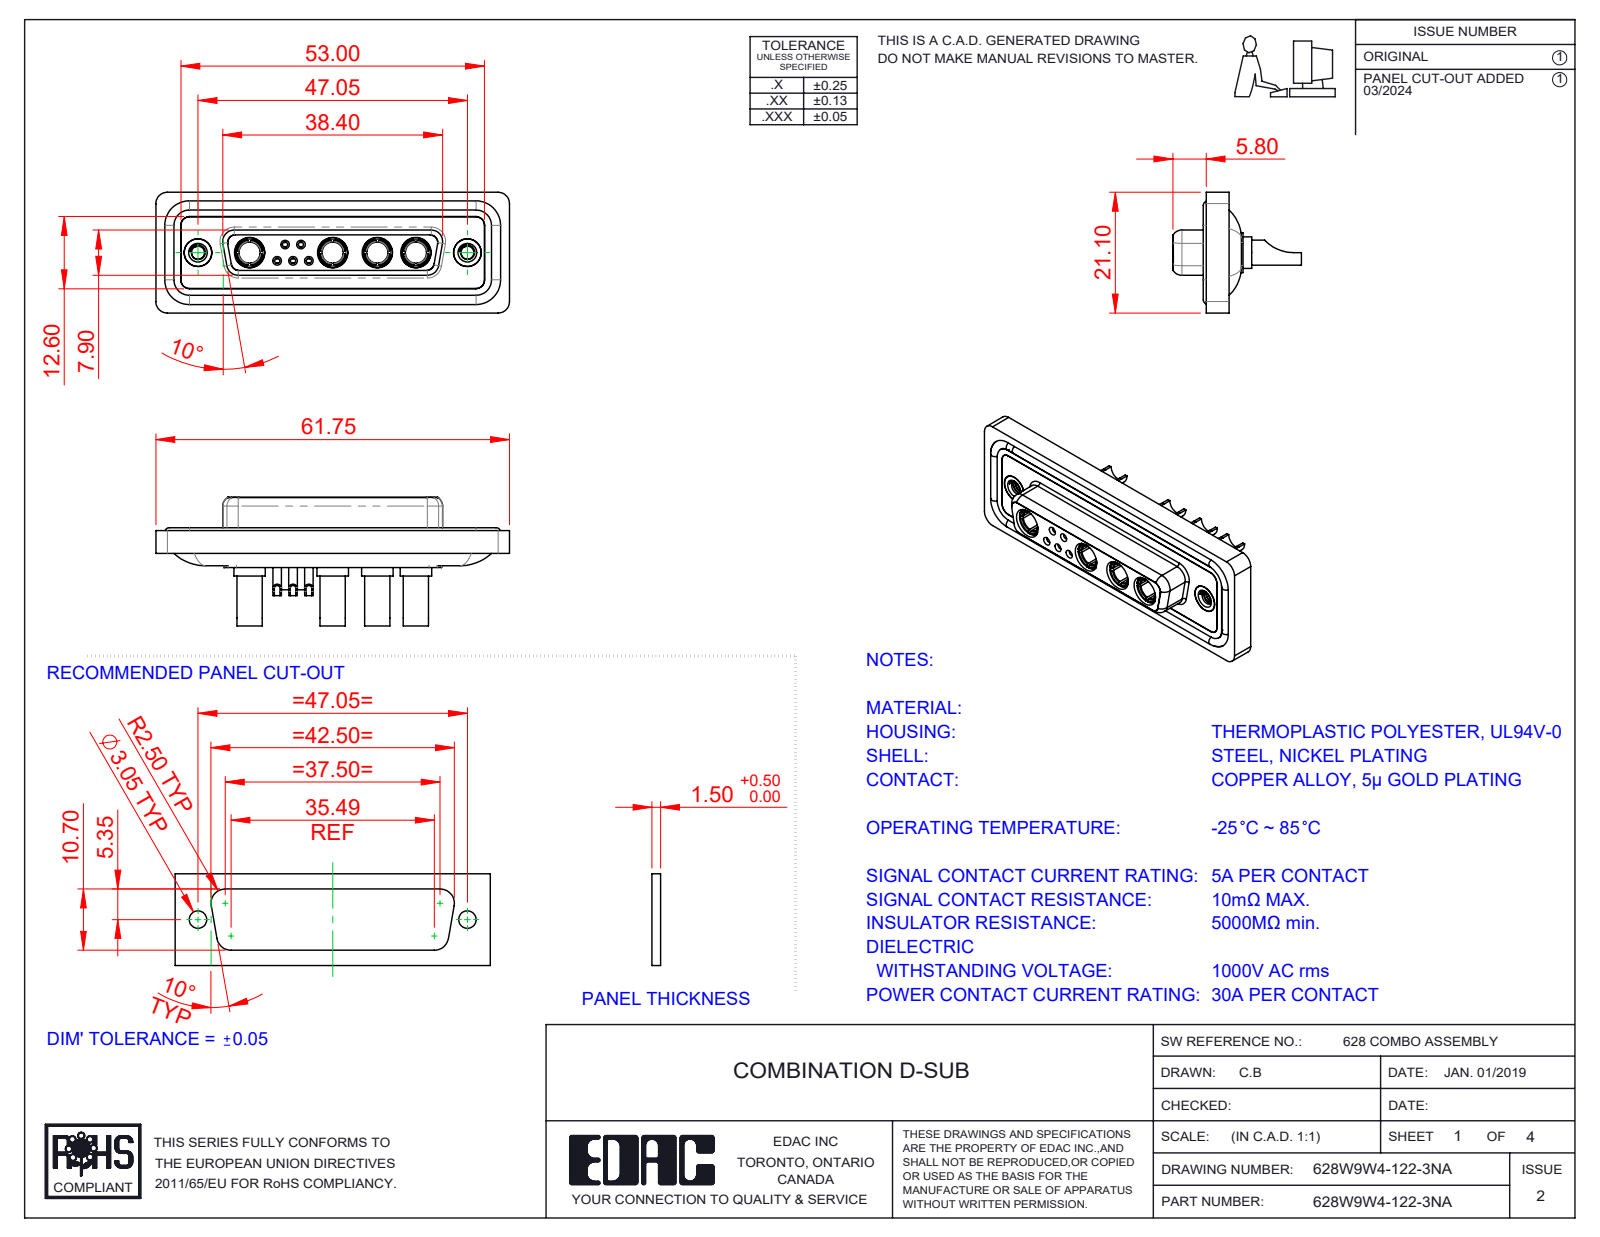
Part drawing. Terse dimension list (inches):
name: 628Combo Threaded Rivet_A; 628Combo Shell Front_25 Contacts; 628Combo Contact Row 2_22; 628Combo Waterproof Housing_25 Contacts (+5 more)
written by: SolidWorks 2023 (CONFIG_CONTROL_DESIGN)
unit: in
bodies: 20 solids, 979 faces (318 planar, 399 cylindrical, 262 other)
size: 2.431 × 0.884 × 0.831
volume: 0.508 in³; area: 21.77 in²
holes: 6× ⌀0.191, 5× ⌀0.035, 5× ⌀0.039, 5× ⌀0.043, 5× ⌀0.059, 5× ⌀0.079, 4× ⌀0.138, 4× ⌀0.146, 4× ⌀0.209, 3× ⌀0.063, 2× ⌀0.067, 2× ⌀0.089
bosses: 6× ⌀0.063, 5× ⌀0.087, 4× ⌀0.217, 4× ⌀0.205, 4× ⌀0.195, 4× ⌀0.187, 4× ⌀0.173, 4× ⌀0.148
rounds: 22× R0.059, 18× R0.079, 8× R0.053, 8× R0.063, 6× R0.039, 4× R0.01, 4× R0.02, 4× R0.024
face distances: 0.016, 0.071, 0.293, 0.222, 0.02, 0.278, 0.26, 0.063, 0.043, 0.114
hole spacings: 0.124, 0.109, 0.198, 0.109, 0.173, 0.198, 0.218, 0.226
